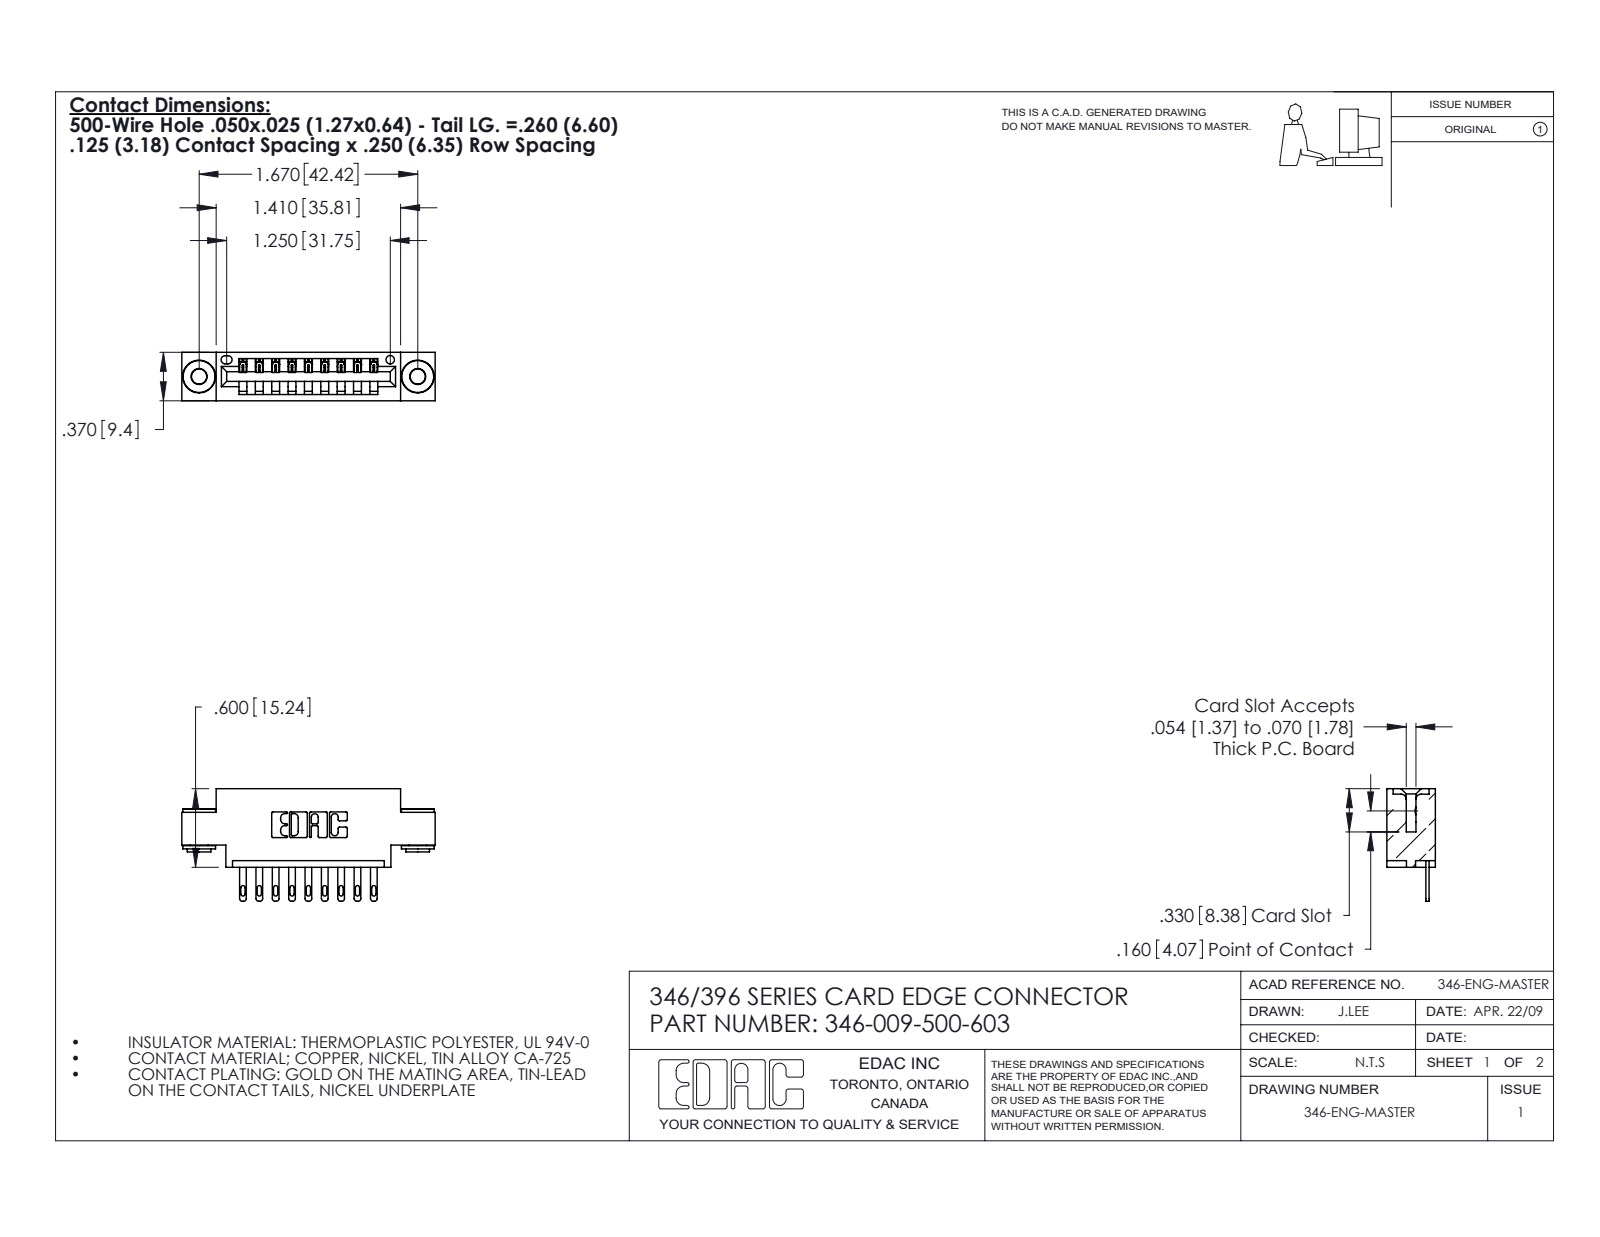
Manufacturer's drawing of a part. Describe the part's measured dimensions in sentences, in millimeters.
The part is named "346-009-500-603; 345-292-001_345-293-100; 346 Part_0.170 Offset - 0.156 Dia-TH; 345-250-002_345-250-002-102". Its 3-D file was written by "SolidWorks 2020 (CONFIG_CONTROL_DESIGN)". It is 12 solids with 664 faces: 410 planar, 246 cylindrical and 8 other. Overall it measures 49.1 by 21.8 by 9.4 millimeters. Its volume is 4 330 cubic millimeters and its surface area 5 488 square millimeters. Round holes: 2 of diameter 2.9, 2 of diameter 4, 1 of diameter 1.6. Round bosses or shafts: 2 of diameter 6.4, 2 of diameter 4.6, 2 of diameter 3.5. Partial cylindrical surfaces (rounded edges, fillets, slot ends): 22 of radius 0.3, 18 of radius 0.2, 18 of radius 0.4, 18 of radius 0.5, 6 of radius 0.2, 6 of radius 0.8, 3 of radius 0.7, 2 of radius 0.8. The main face-to-face distances are 6.4, 9.4, 1.2, 8.2, 0.6, 1.8, 7.6, 5.6, 3.8, 2.5. The hole center spacings are 6.2, 37.2, 42.4.
